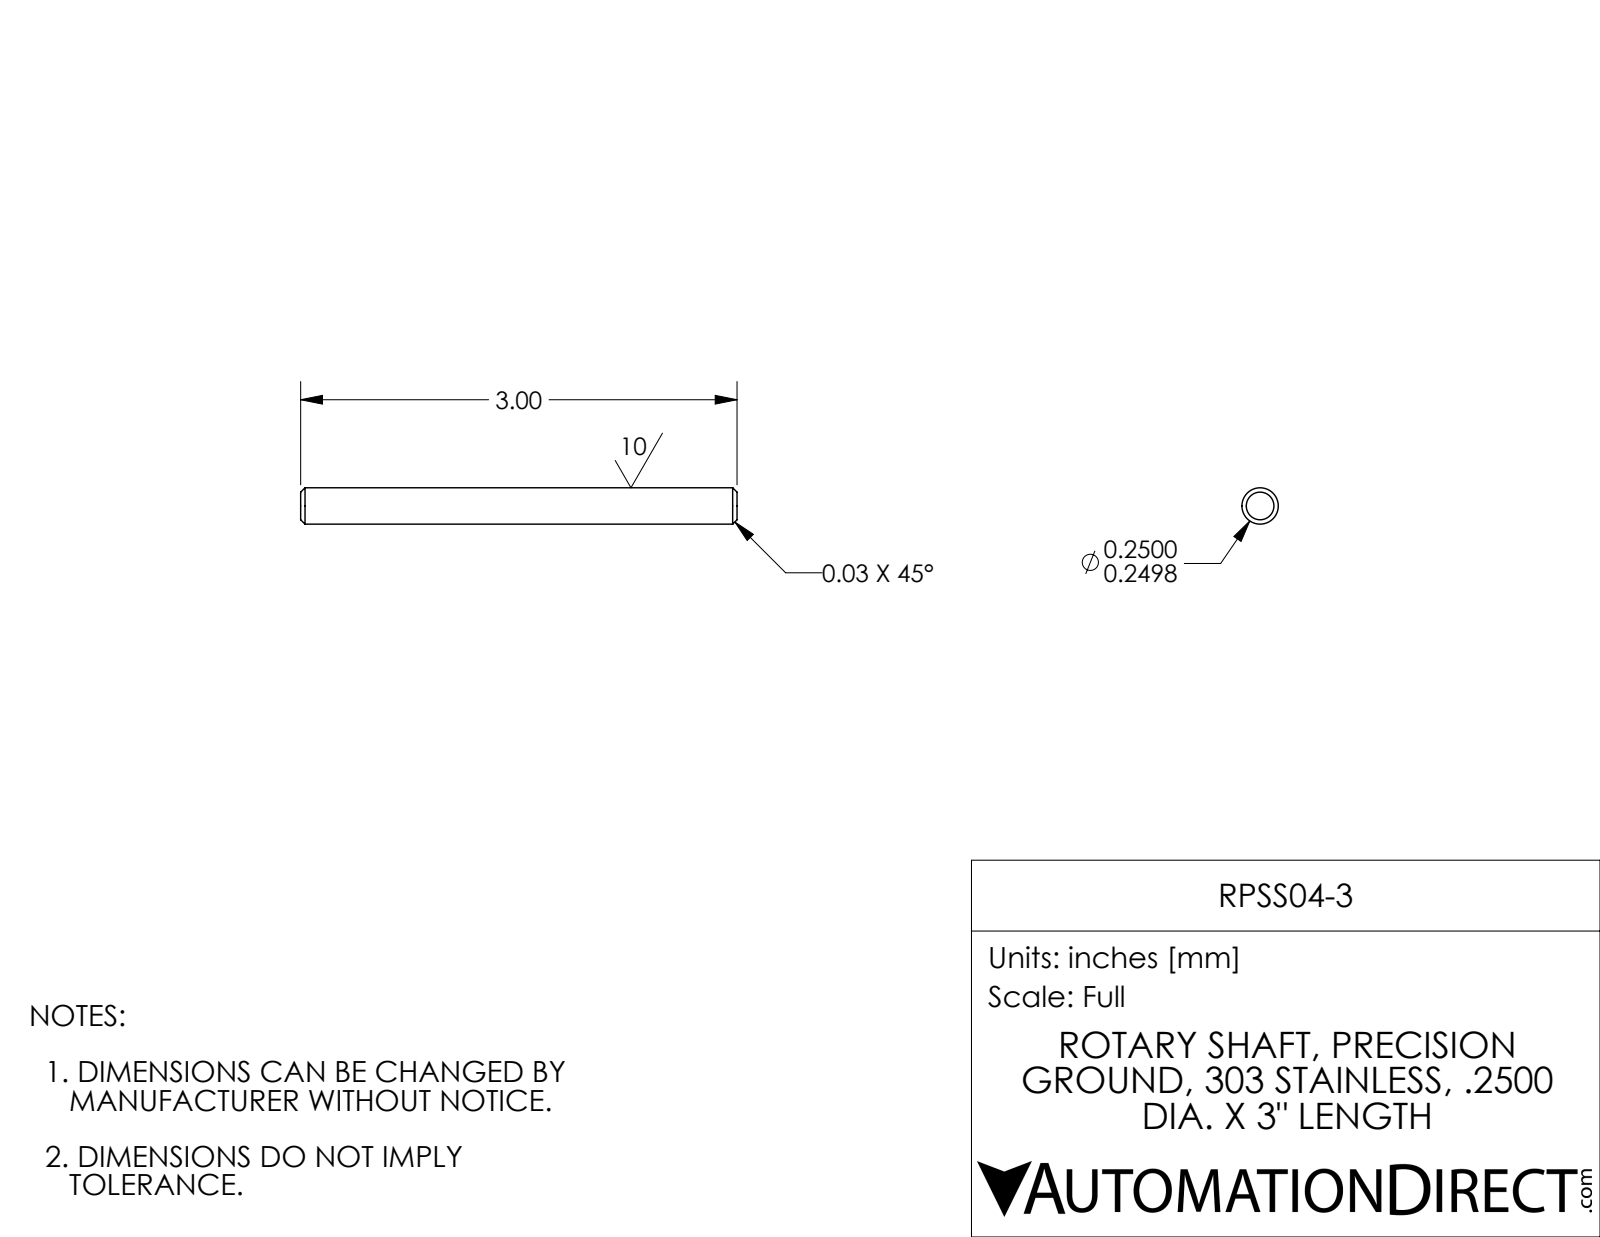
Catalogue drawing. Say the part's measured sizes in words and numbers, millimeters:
The part is named "RPSS04-3". Its 3-D file was written by "SolidWorks 2017 (AUTOMOTIVE_DESIGN)". It is 1 solid with 8 faces: 2 planar, 2 cylindrical and 4 other. Overall it measures 76.2 by 6.4 by 6.4 millimeters. Its volume is 2 410 cubic millimeters and its surface area 1 564 square millimeters. Round bosses or shafts: 1 of diameter 6.4. The main face-to-face distances are 76.2.
